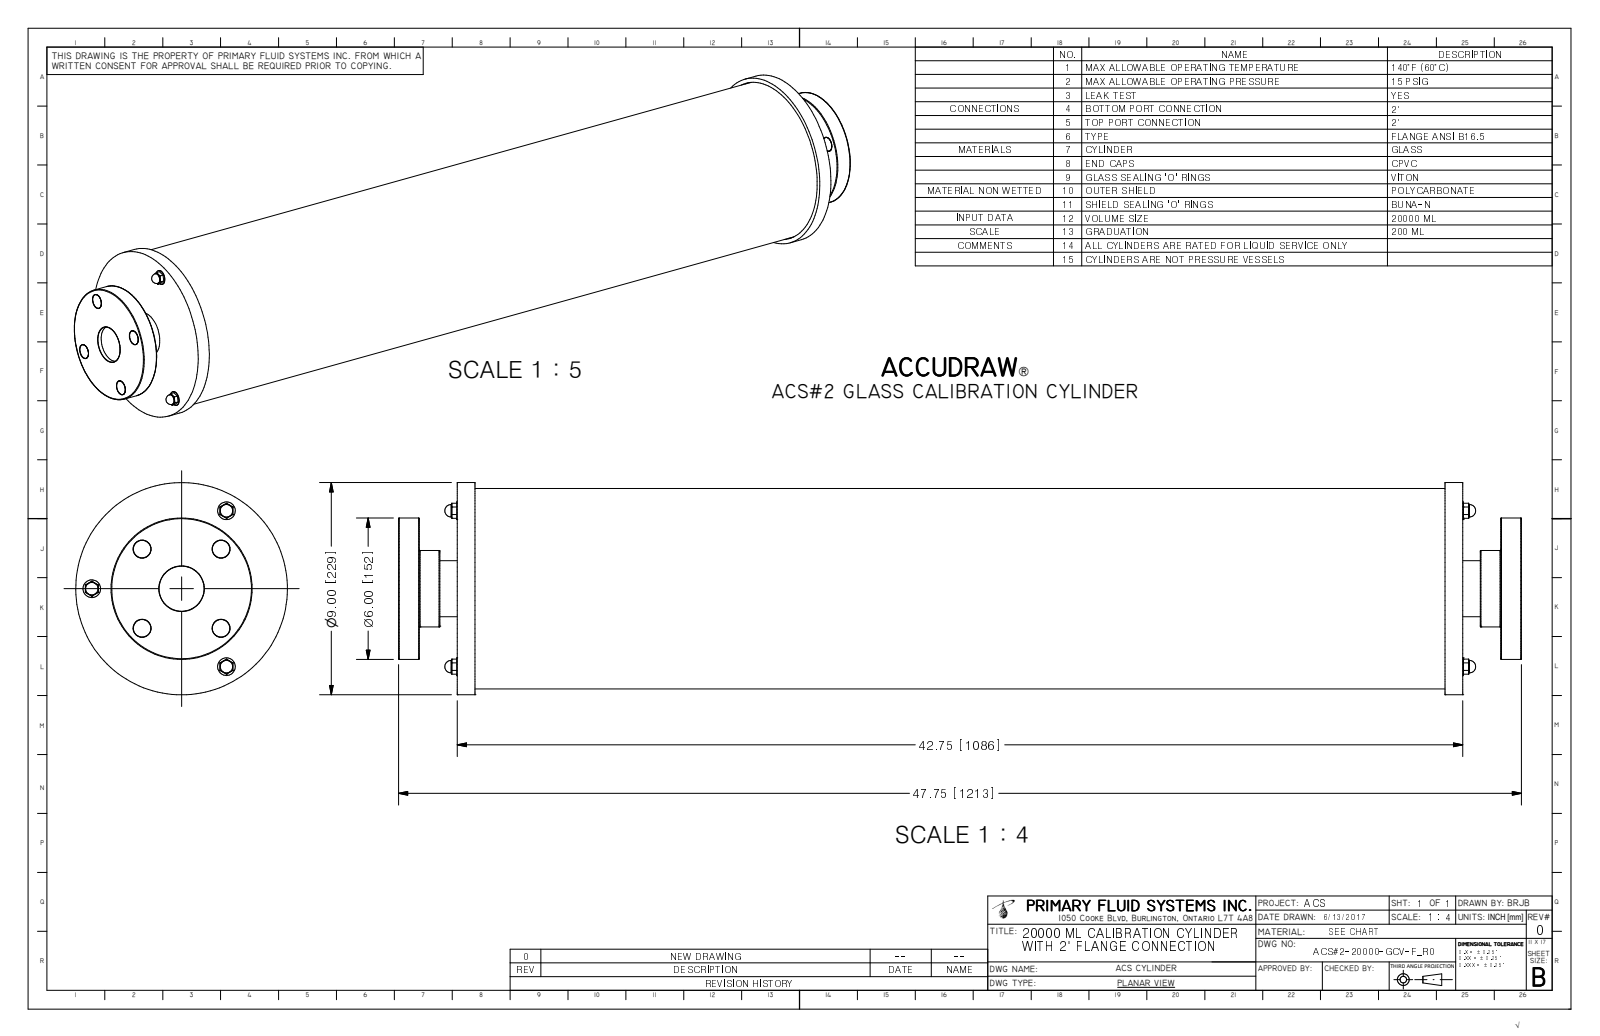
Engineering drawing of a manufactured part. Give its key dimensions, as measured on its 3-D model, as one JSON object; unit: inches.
{"part_name": "ACS#2-20000-GCV-F_R0", "step_written_by": "Autodesk Inventor 2009 (AUTOMOTIVE_DESIGN)", "units": "inches", "bodies": {"solids": 1, "faces": 207, "planar": 70, "cylindrical": 87, "other": 50}, "overall_size": [47.75, 9, 9], "volume_in3": 2488, "surface_area_in2": 1532, "round_holes": [[0.745, 4], [1.913, 1], [1.939, 1]], "round_bosses_or_shafts": [[0.75, 3], [0.528, 3], [9, 1], [8.5, 1], [6, 1], [3.244, 1], [2.375, 1]], "partial_cylinders_radius": [[0.005, 42]], "face_to_face_distances": [42.75, 2.5, 45.25, 0.885, 46.865, 1.615, 44.365, 47.75, 45.98, 42], "hole_center_spacings": [2.375, 3.359, 4.75]}
